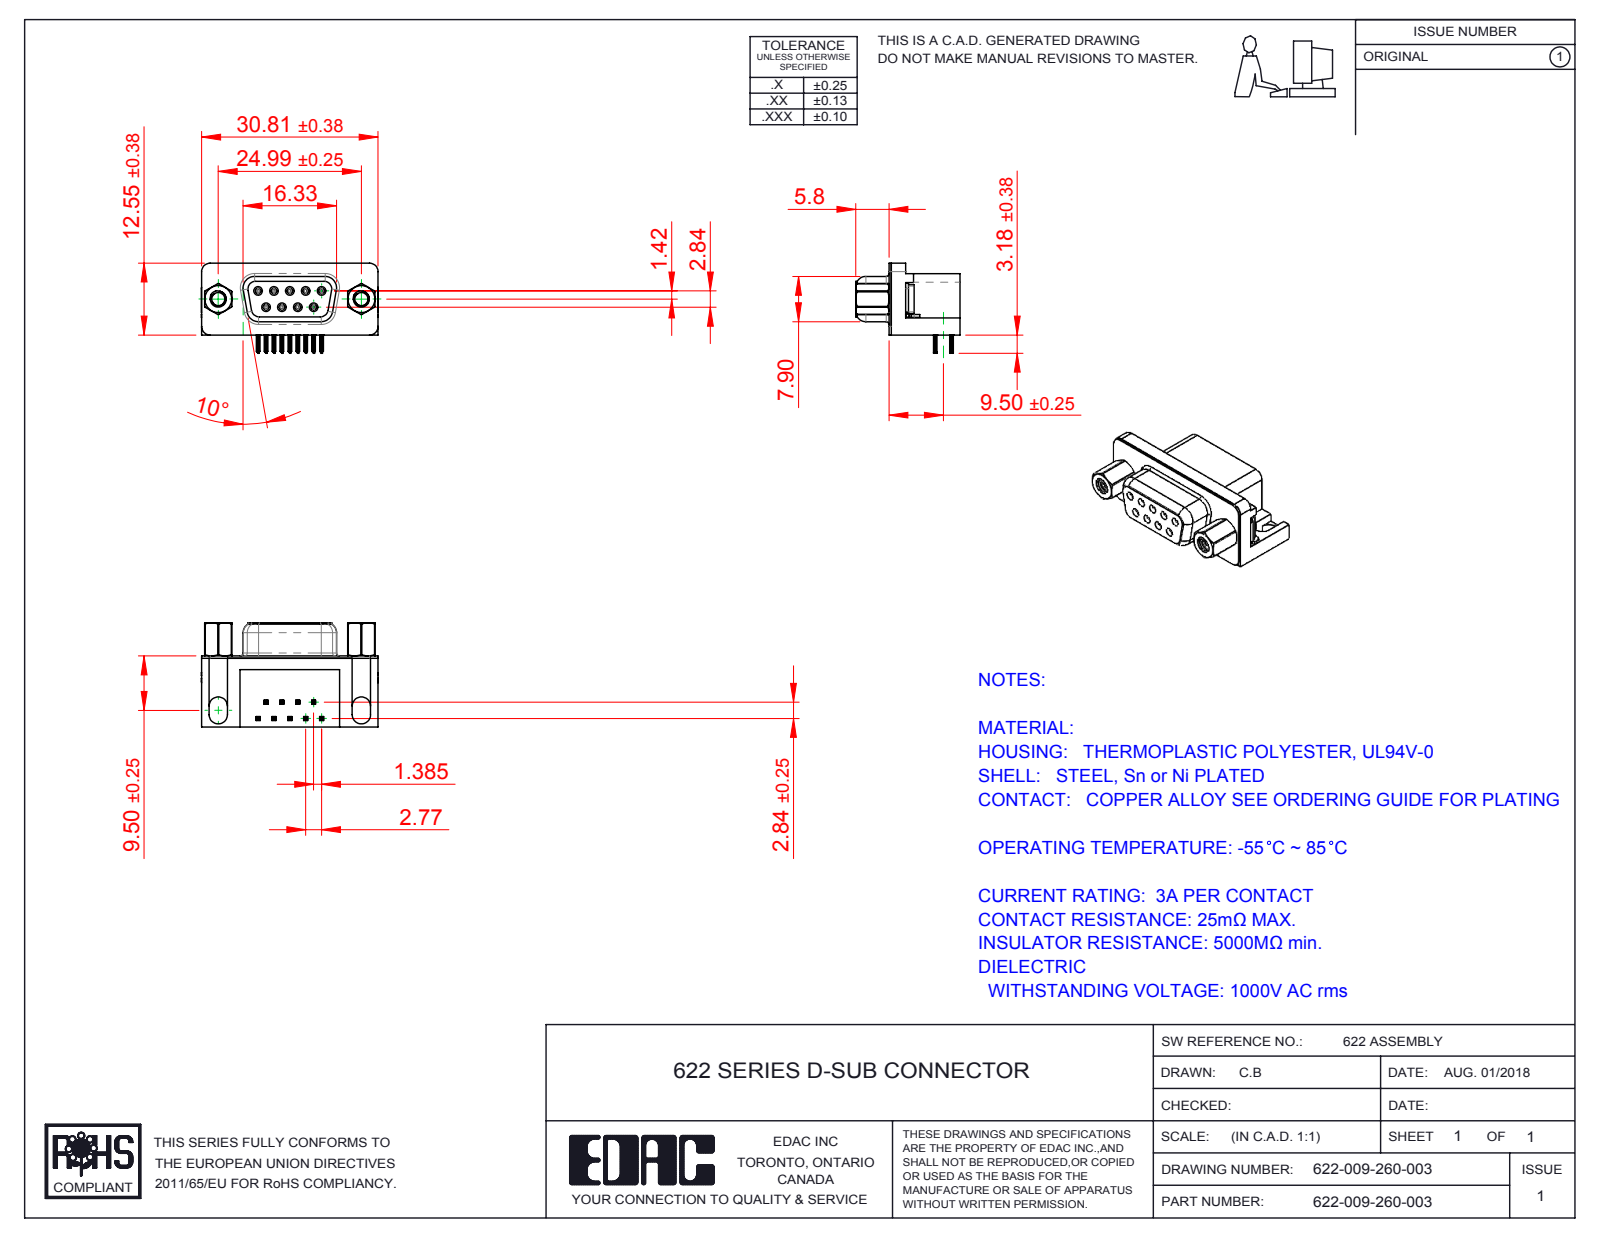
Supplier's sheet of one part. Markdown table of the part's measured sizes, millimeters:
| quantity | value |
| --- | --- |
| part name | 622 Housing_9 Socket; 622 Shell_9 Socket; 622 4-40 Hex Standoff 5; 622 Socket Bottom (+4 more) |
| STEP written by | SolidWorks 2016 (CONFIG_CONTROL_DESIGN) |
| units | millimeters |
| bodies | 17 solids, 1688 faces (706 planar, 476 cylindrical, 506 other) |
| overall size | 30.89 × 18.2 × 15.73 |
| volume | 3 892 mm³ |
| surface area | 5 354 mm² |
| round holes (diameter × count) | 0.8 × 9, 0.9 × 9, 2.26 × 2, 2.29 × 2, 4 × 2, 4.8 × 2, 5 × 2 |
| round bosses / shafts (diameter × count) | 1.2 × 9, 4.9 × 2, 4.75 × 2, 3.9 × 2, 2.79 × 2 |
| partial cylindrical surfaces (radius × count) | 0.1 × 72, 0.15 × 36, 0.35 × 18, 1 × 18, 0.34 × 9, 0.25 × 8, 1.35 × 8, 1.6 × 8 |
| main face-to-face distances | 0.4, 12, 12.4, 6.2, 2.9, 2.5, 10.34, 0.35, 9.5, 10.69 |
| hole center spacings | 3.16, 2.77, 5.54, 5.03, 5.04, 8.31, 7.48, 7.49 |
